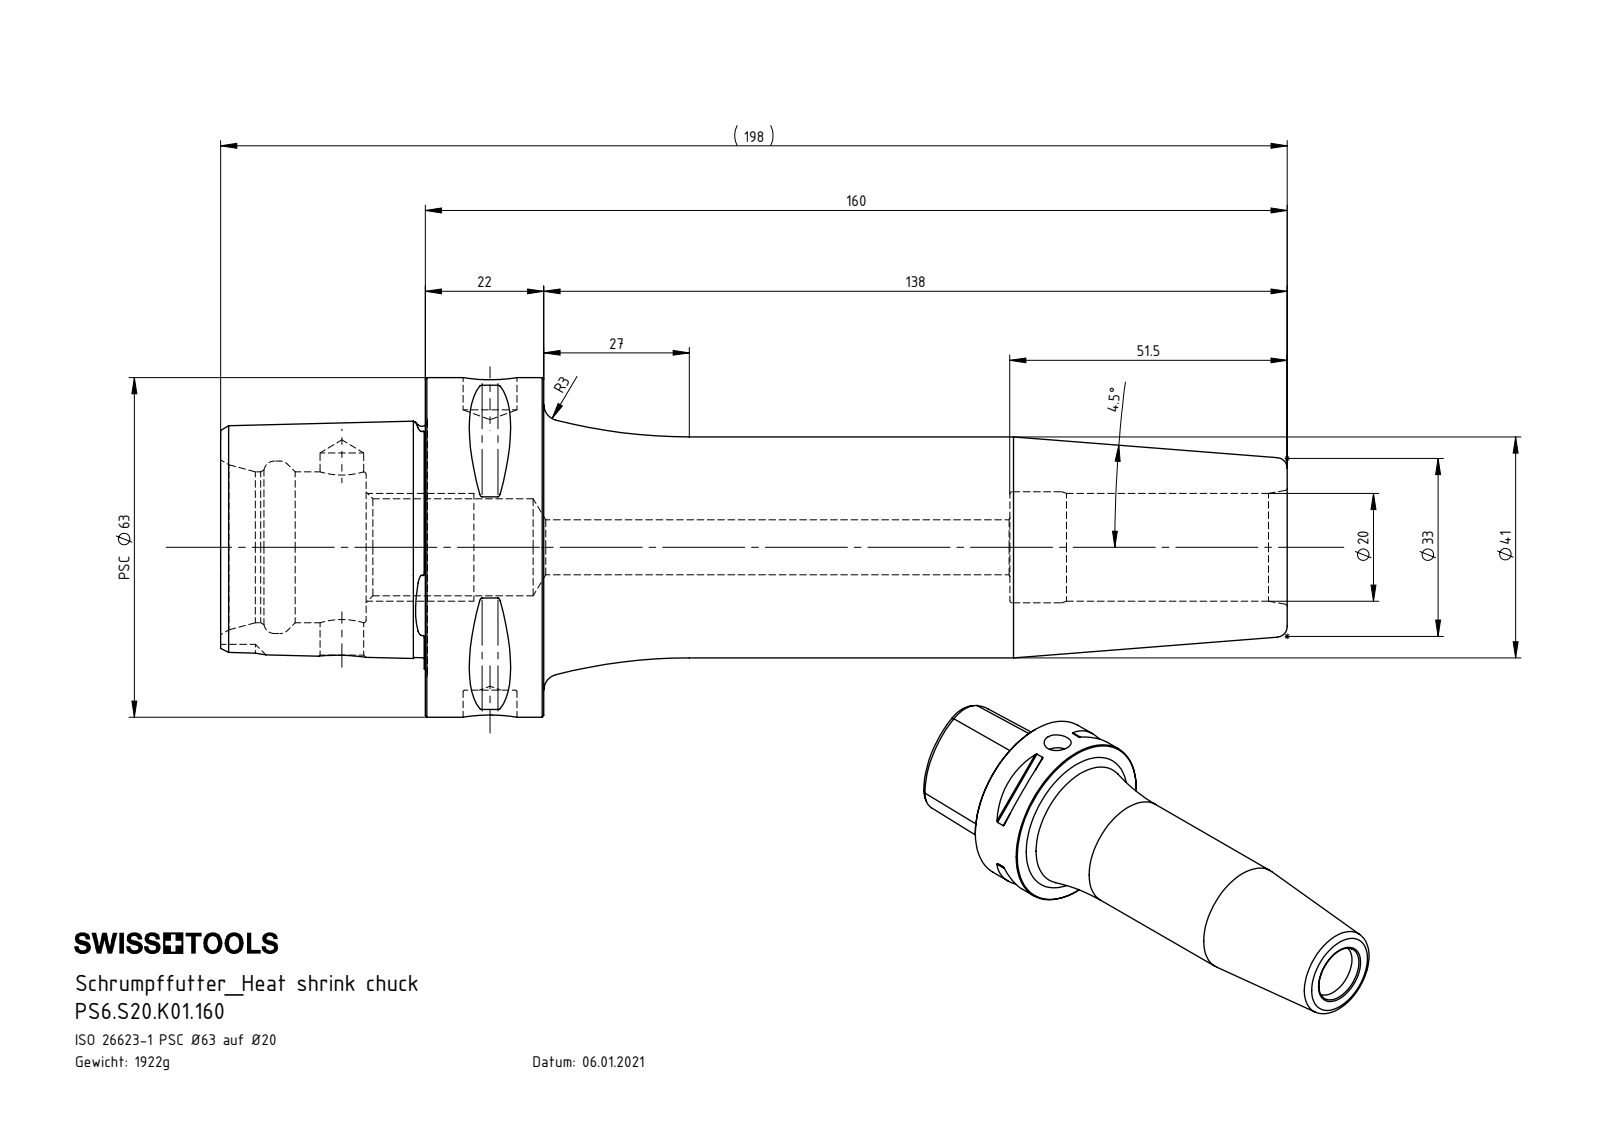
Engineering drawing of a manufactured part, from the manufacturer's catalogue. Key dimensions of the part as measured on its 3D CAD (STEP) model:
Part name (STEP PRODUCT): PS6.S20.K01.160
STEP written by: SolidWorks 2022 (AUTOMOTIVE_DESIGN)
Units: millimetres
Bodies: 1 solid, 154 faces (22 planar, 35 cylindrical, 97 other)
Overall size (bounding box): 198 × 63 × 63
Volume: 244 823 mm³ · Surface area: 42 587 mm²
Round holes (diameter × count): ⌀8.1 ×1, ⌀10 ×1, ⌀10.2 ×1, ⌀18 ×1, ⌀20 ×1, ⌀20.6 ×1, ⌀28 ×1, ⌀32 ×1
Round bosses / shafts (diameter × count): ⌀63 ×1, ⌀41 ×1
Partial cylindrical surfaces — rounded edges, fillets, slot ends (radius × count): R0.5 ×8, R6 ×1
Main face-to-face distances: 22, 38, 60, 24.88, 198, 160, 138, 27, 11, 33
Hole centre spacings: 27.5
